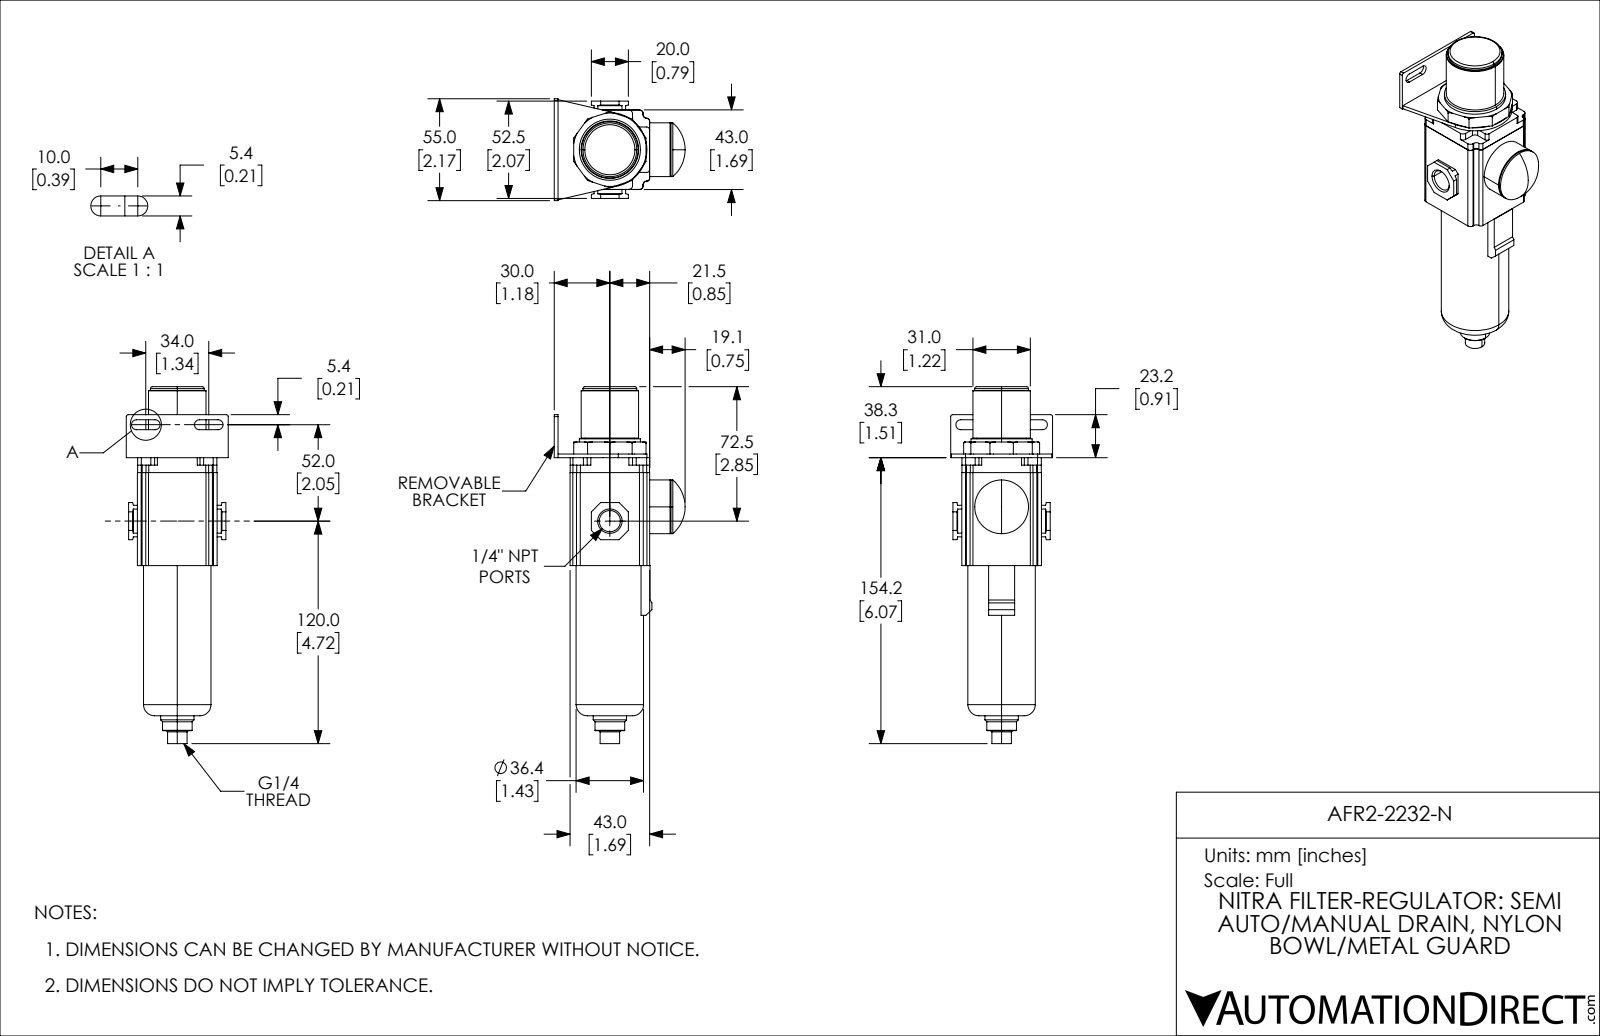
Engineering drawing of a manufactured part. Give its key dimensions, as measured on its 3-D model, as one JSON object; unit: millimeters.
{"part_name": "AFR2-2232-N", "step_written_by": "SolidWorks 2019 (CONFIG_CONTROL_DESIGN)", "units": "millimeters", "bodies": {"solids": 1, "faces": 220, "planar": 119, "cylindrical": 69, "other": 32}, "overall_size": [192.5, 70.62, 55], "volume_mm3": 237290, "surface_area_mm2": 34102, "round_holes": [[4.13, 1], [11.45, 1]], "round_bosses_or_shafts": [[29, 2], [36.4, 1], [33, 1], [31, 1], [26.78, 1], [18, 1], [16, 1], [10.5, 1]], "partial_cylinders_radius": [[2, 24], [1.5, 12], [2.7, 4], [1, 2], [20, 1]], "face_to_face_distances": [43, 2, 8.5, 6.5, 49.5, 51.5, 42.9, 36.3, 58.2, 60.2]}
